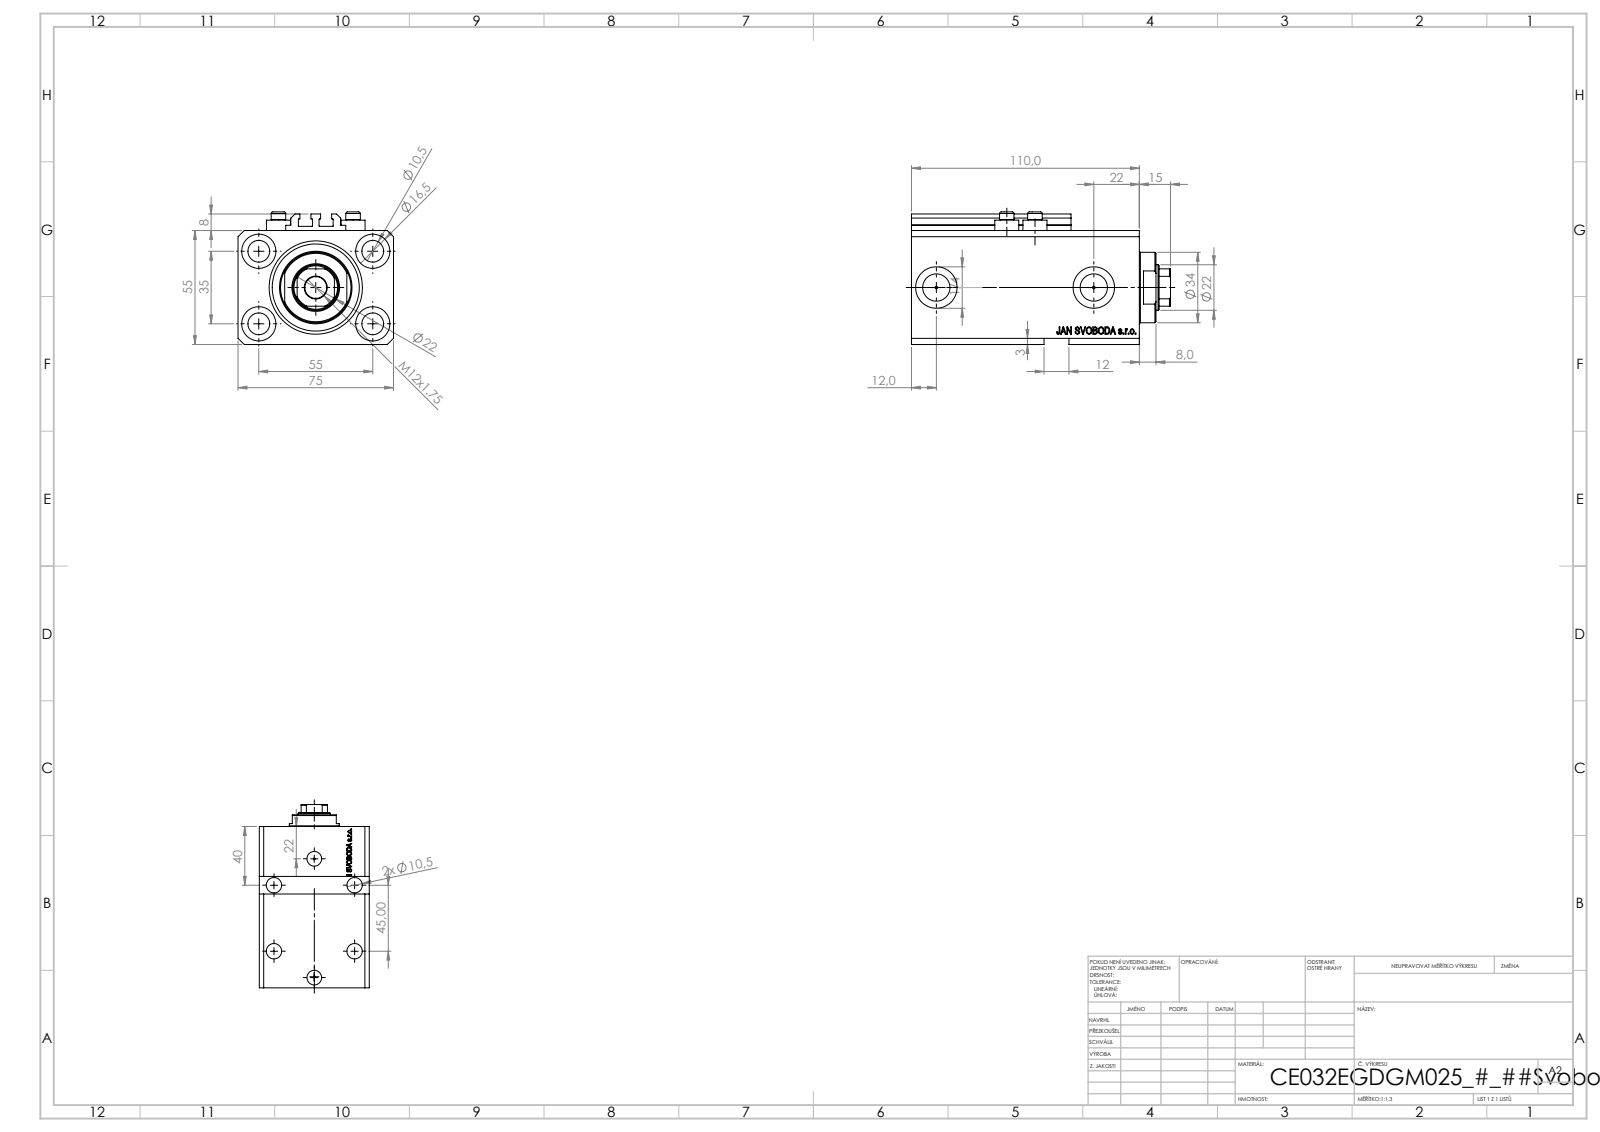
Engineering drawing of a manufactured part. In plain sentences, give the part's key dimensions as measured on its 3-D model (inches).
The part is named "V250CE_E_Body; V250CE_VC_E; V250CE_C_VCP; ALLEN BOLT V250CE". Its 3-D file was written by "SolidWorks 2019 (CONFIG_CONTROL_DESIGN)". It is 8 solids with 1100 faces: 518 planar, 158 cylindrical and 424 other. Overall it measures 4.921 by 2.953 by 2.52 inches. Its volume is 23.05 cubic inches and its surface area 150 square inches. Round holes: 9 of diameter 0.413, 4 of diameter 0.049, 4 of diameter 0.157, 4 of diameter 0.65, 2 of diameter 0.394, 2 of diameter 0.518, 2 of diameter 0.787, 1 of diameter 0.866, 1 of diameter 1.26, 1 of diameter 1.772. Round bosses or shafts: 4 of diameter 0.457, 4 of diameter 0.276, 1 of diameter 1.339. Partial cylindrical surfaces (rounded edges, fillets, slot ends): 10 of radius 0.008, 1 of radius 0.413. The main face-to-face distances are 2.165, 2.953, 0.591, 4.331, 3.74, 0.39, 0.118, 3.35, 3.941, 2.244. The hole center spacings are 1.283, 1.294, 2.165, 2.706, 0.535, 0.555, 0.907, 1.016.
